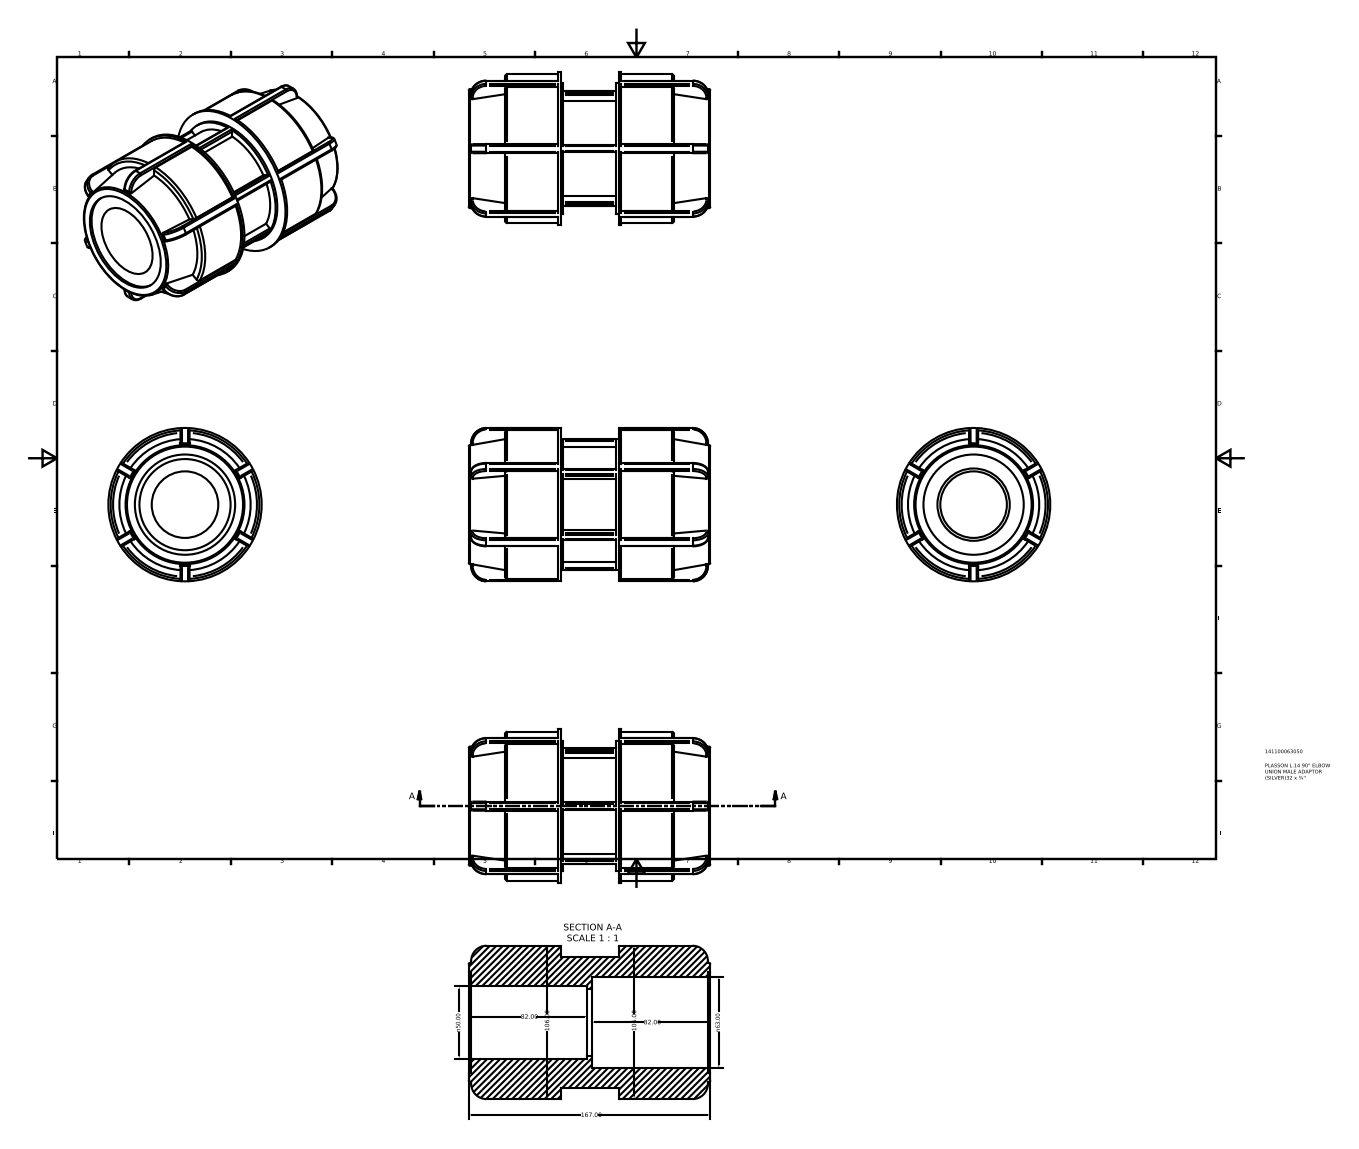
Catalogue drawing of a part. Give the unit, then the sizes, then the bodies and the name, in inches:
Units: inches
Overall size (bounding box): 6.575 × 4.173 × 4.173
Round holes (diameter × count): ⌀1.811 ×1, ⌀1.969 ×1, ⌀2.48 ×1, ⌀2.728 ×1
Round bosses / shafts (diameter × count): ⌀4.173 ×1, ⌀4.048 ×1, ⌀3.547 ×1, ⌀3.13 ×1
Partial cylindrical surfaces — rounded edges, fillets, slot ends (radius × count): R0.042 ×44
Main face-to-face distances: 1.578, 0.066, 4.011, 1.512, 2.498, 4.076, 2.433, 2.564, 0.248, 0.986
Volume: 44.92 in³ · Surface area: 162.7 in²
Bodies: 1 solid, 230 faces (92 planar, 86 cylindrical, 52 other)
Part name (STEP PRODUCT): 141100063050
STEP written by: Autodesk Inventor 2015 (AUTOMOTIVE_DESIGN)
